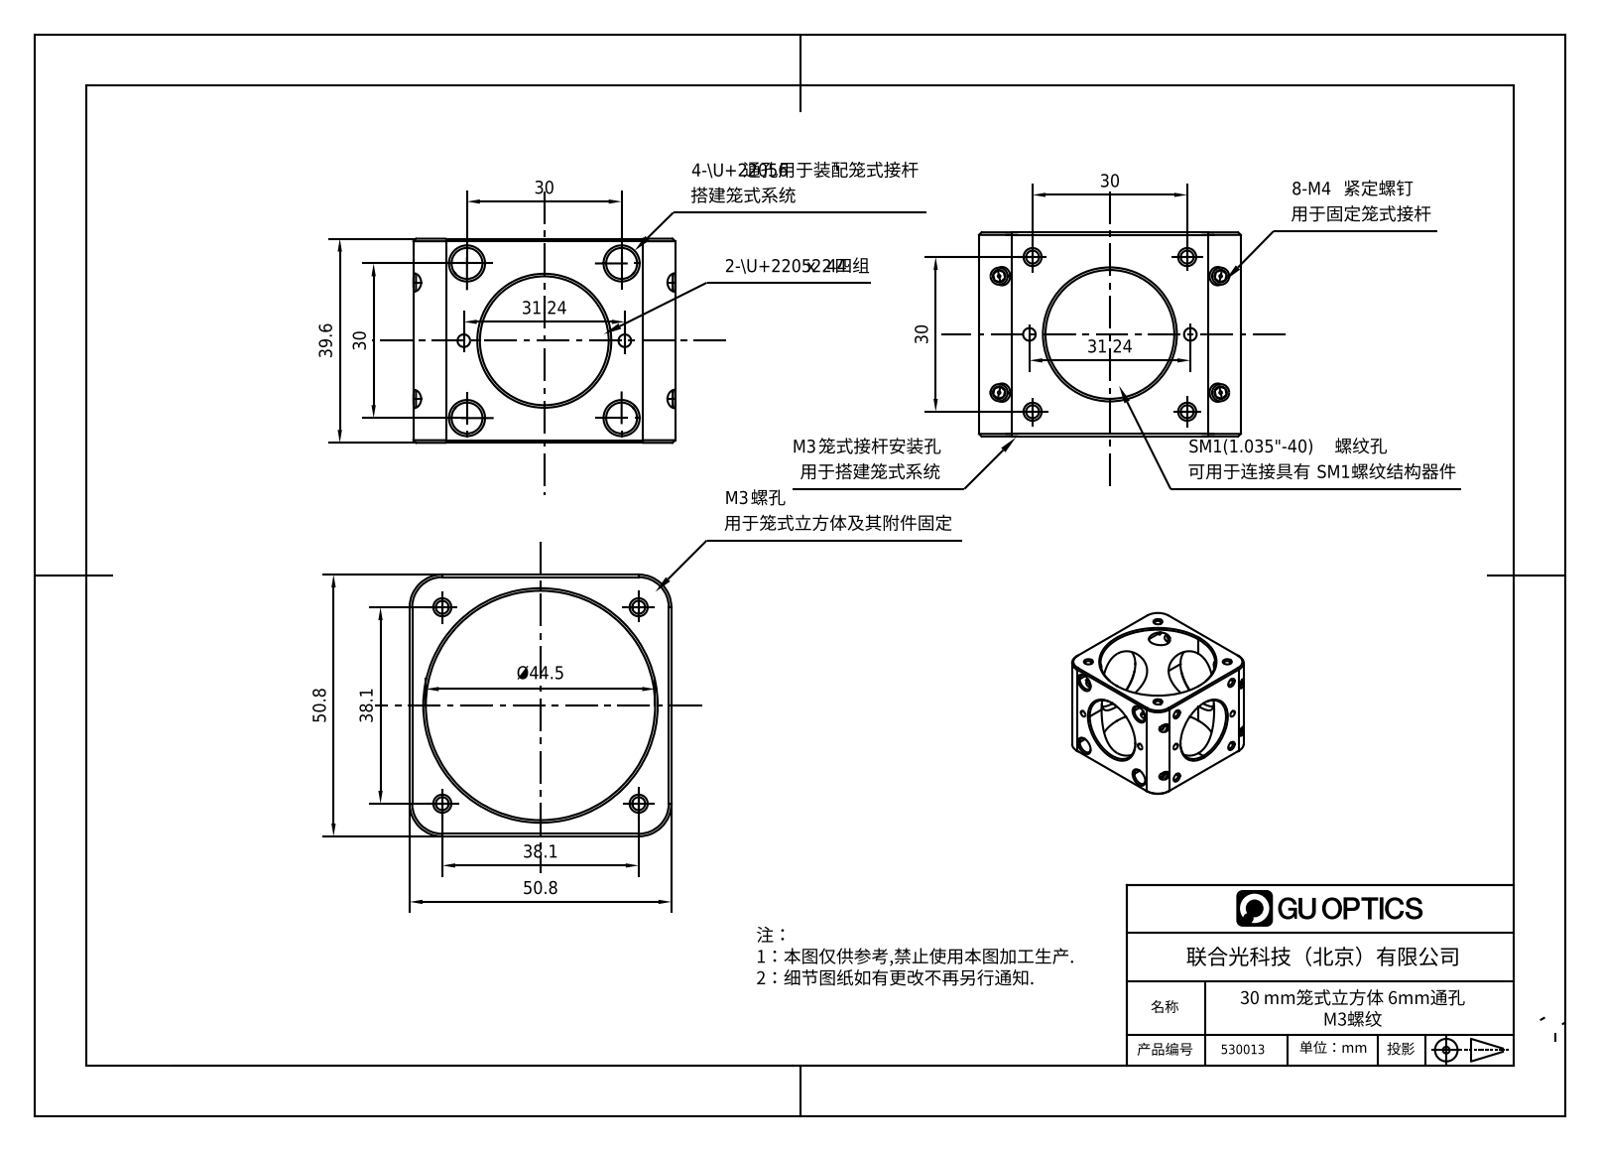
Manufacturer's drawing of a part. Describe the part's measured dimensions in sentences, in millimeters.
The part is named "2.2.7.4_L30F-TM_30 mm笼式立方体，带6mm通孔，带M3螺纹". Its 3-D file was written by "SolidWorks 2018 (AUTOMOTIVE_DESIGN)". It is 0 solids with 348 faces: 78 planar, 94 cylindrical and 176 other. Overall it measures 50.8 by 50.8 by 39.6 millimeters. Round holes: 8 of diameter 2.5, 4 of diameter 2.44, 4 of diameter 3.3, 4 of diameter 6, 2 of diameter 25, 1 of diameter 44.5. Partial cylindrical surfaces (rounded edges, fillets, slot ends): 4 of radius 6.35. The main face-to-face distances are 50.8, 39.6, 63.2, 2.1, 1.66, 49.14, 45.6, 8.32, 37.3, 47.48. The hole center spacings are 15.01, 21.21, 30, 34.1, 7.48, 12.74, 15.62, 24.29.
